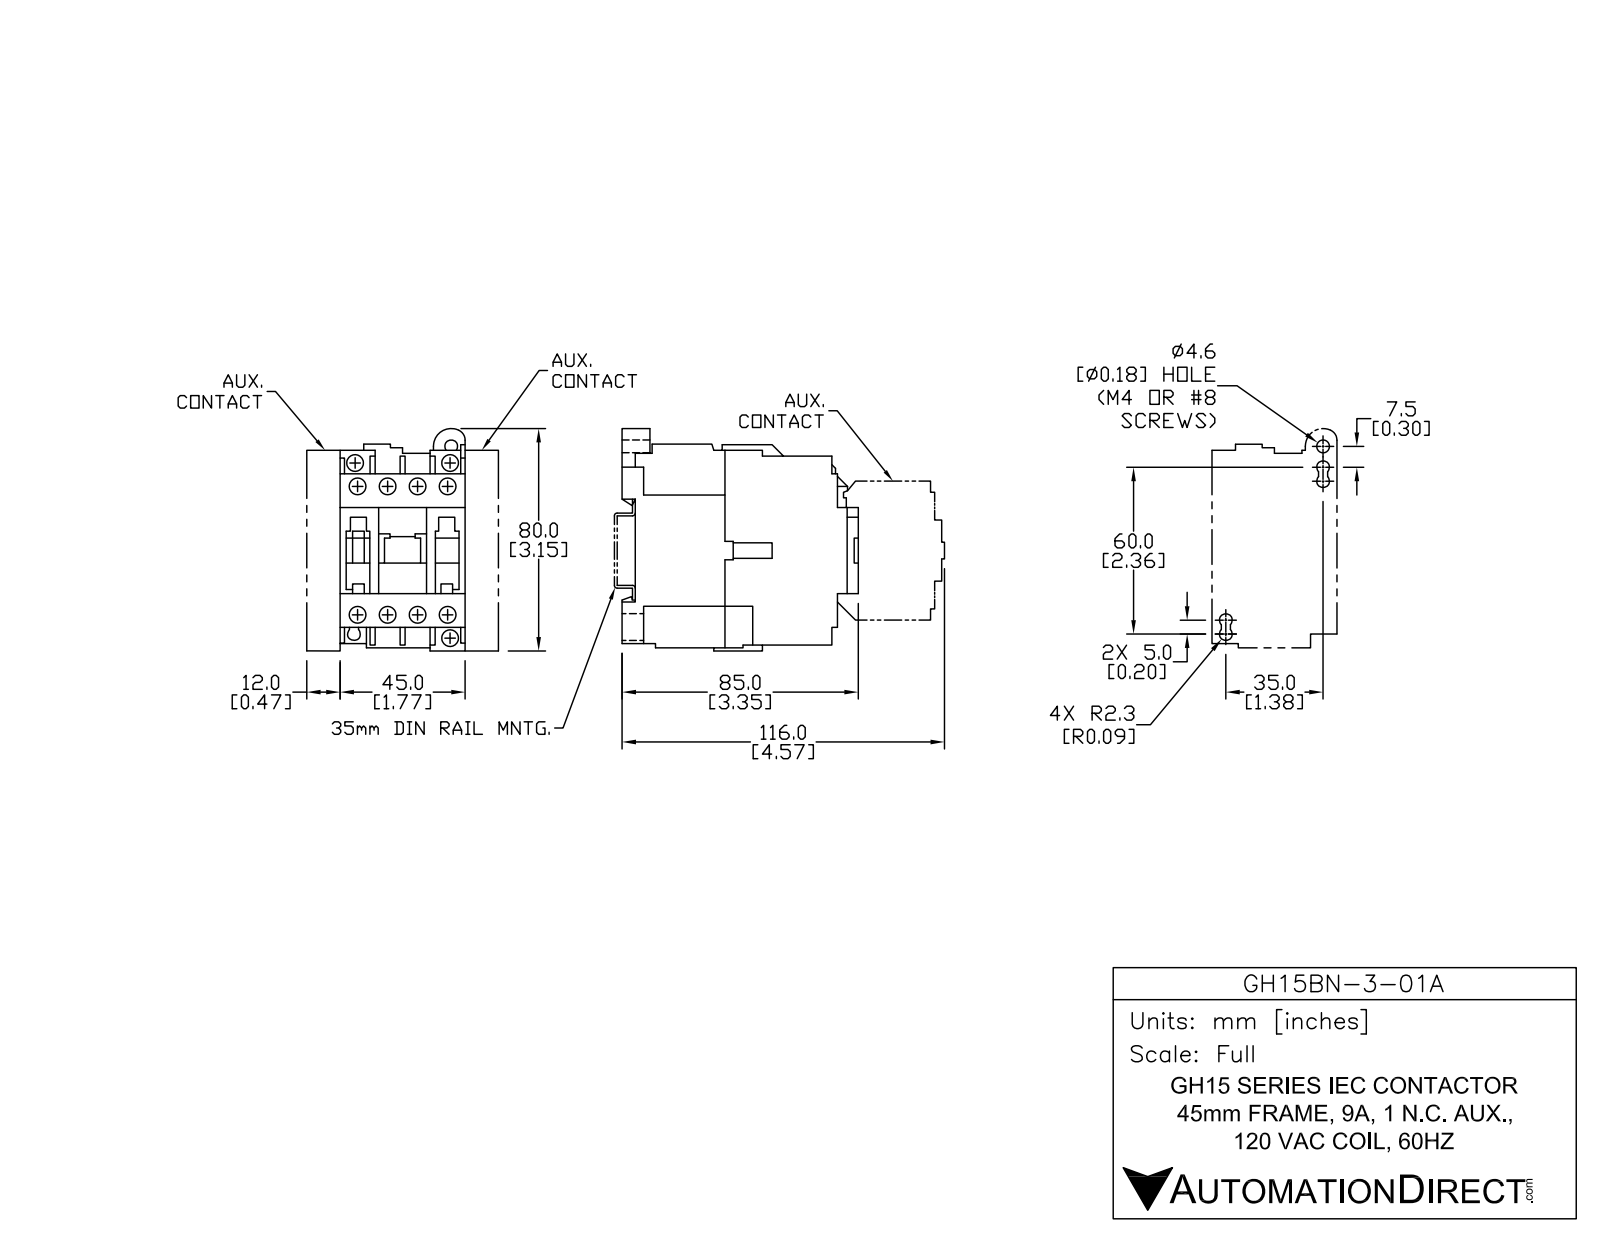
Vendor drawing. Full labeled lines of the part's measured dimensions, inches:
Part name (STEP PRODUCT): GH15BN-3-01A
STEP written by: SolidWorks 2009 (AUTOMOTIVE_DESIGN)
Units: inches
Bodies: 1 solid, 672 faces (451 planar, 65 cylindrical, 156 other)
Overall size (bounding box): 3.366 × 3.15 × 1.772
Volume: 11.98 in³ · Surface area: 55.48 in²
Round holes (diameter × count): ⌀0.246 ×9, ⌀0.256 ×2, ⌀0.181 ×1
Partial cylindrical surfaces — rounded edges, fillets, slot ends (radius × count): R0.039 ×10, R0.091 ×8, R0.187 ×8, R0.118 ×2, R0.196 ×1, R0.197 ×1
Main face-to-face distances: 1.772, 0.374, 1.398, 0.477, 0.92, 0.315, 0.276, 1.329, 0.409, 1.294
Hole centre spacings: 0.443, 1.855, 0.886, 1.802, 2.007, 0.3, 1.329, 2.102
